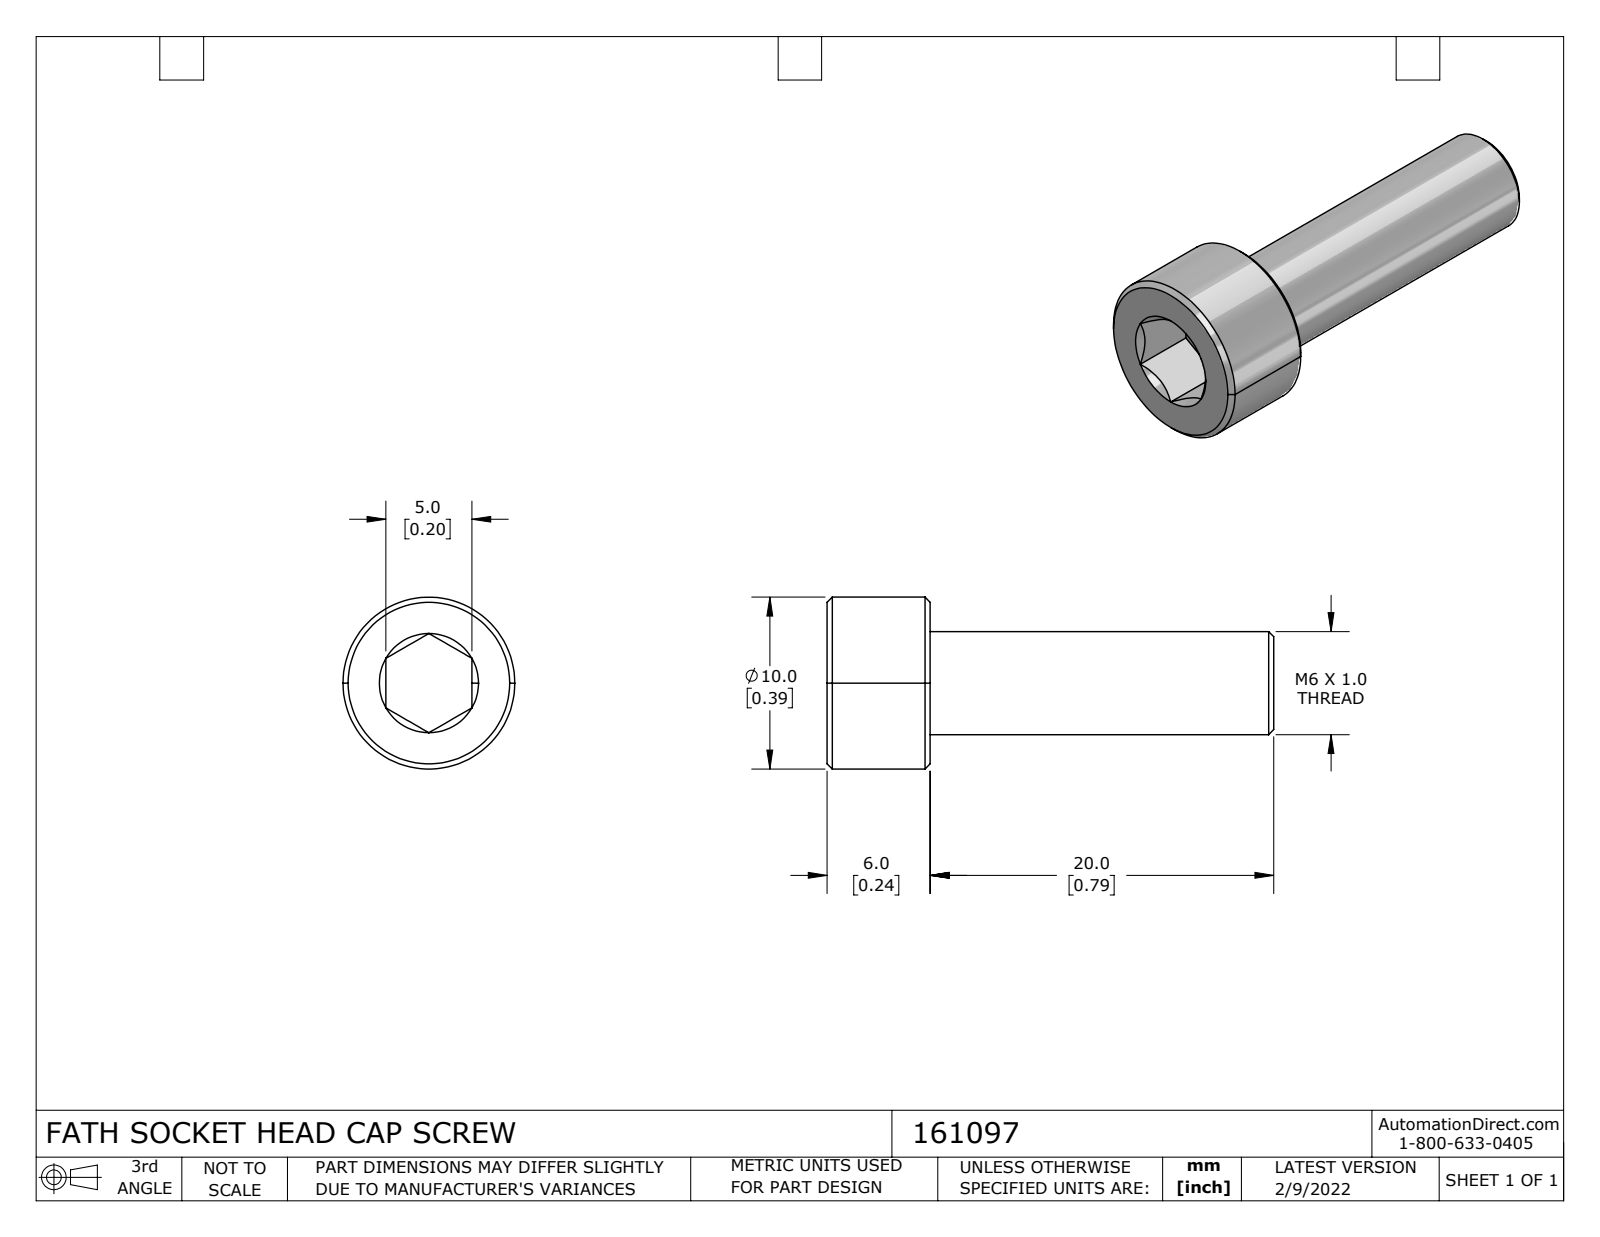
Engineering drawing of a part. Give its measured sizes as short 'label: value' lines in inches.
name: 161097
written by: SolidWorks 2021 (CONFIG_CONTROL_DESIGN)
unit: in
bodies: 1 solid, 27 faces (10 planar, 4 cylindrical, 13 other)
size: 1.024 × 0.394 × 0.394
volume: 0.058 in³; area: 1.19 in²
bosses: 1× ⌀0.394, 1× ⌀0.236
face distances: 0.236, 0.197, 1.024, 0.787, 0.148, 0.089, 0.876
